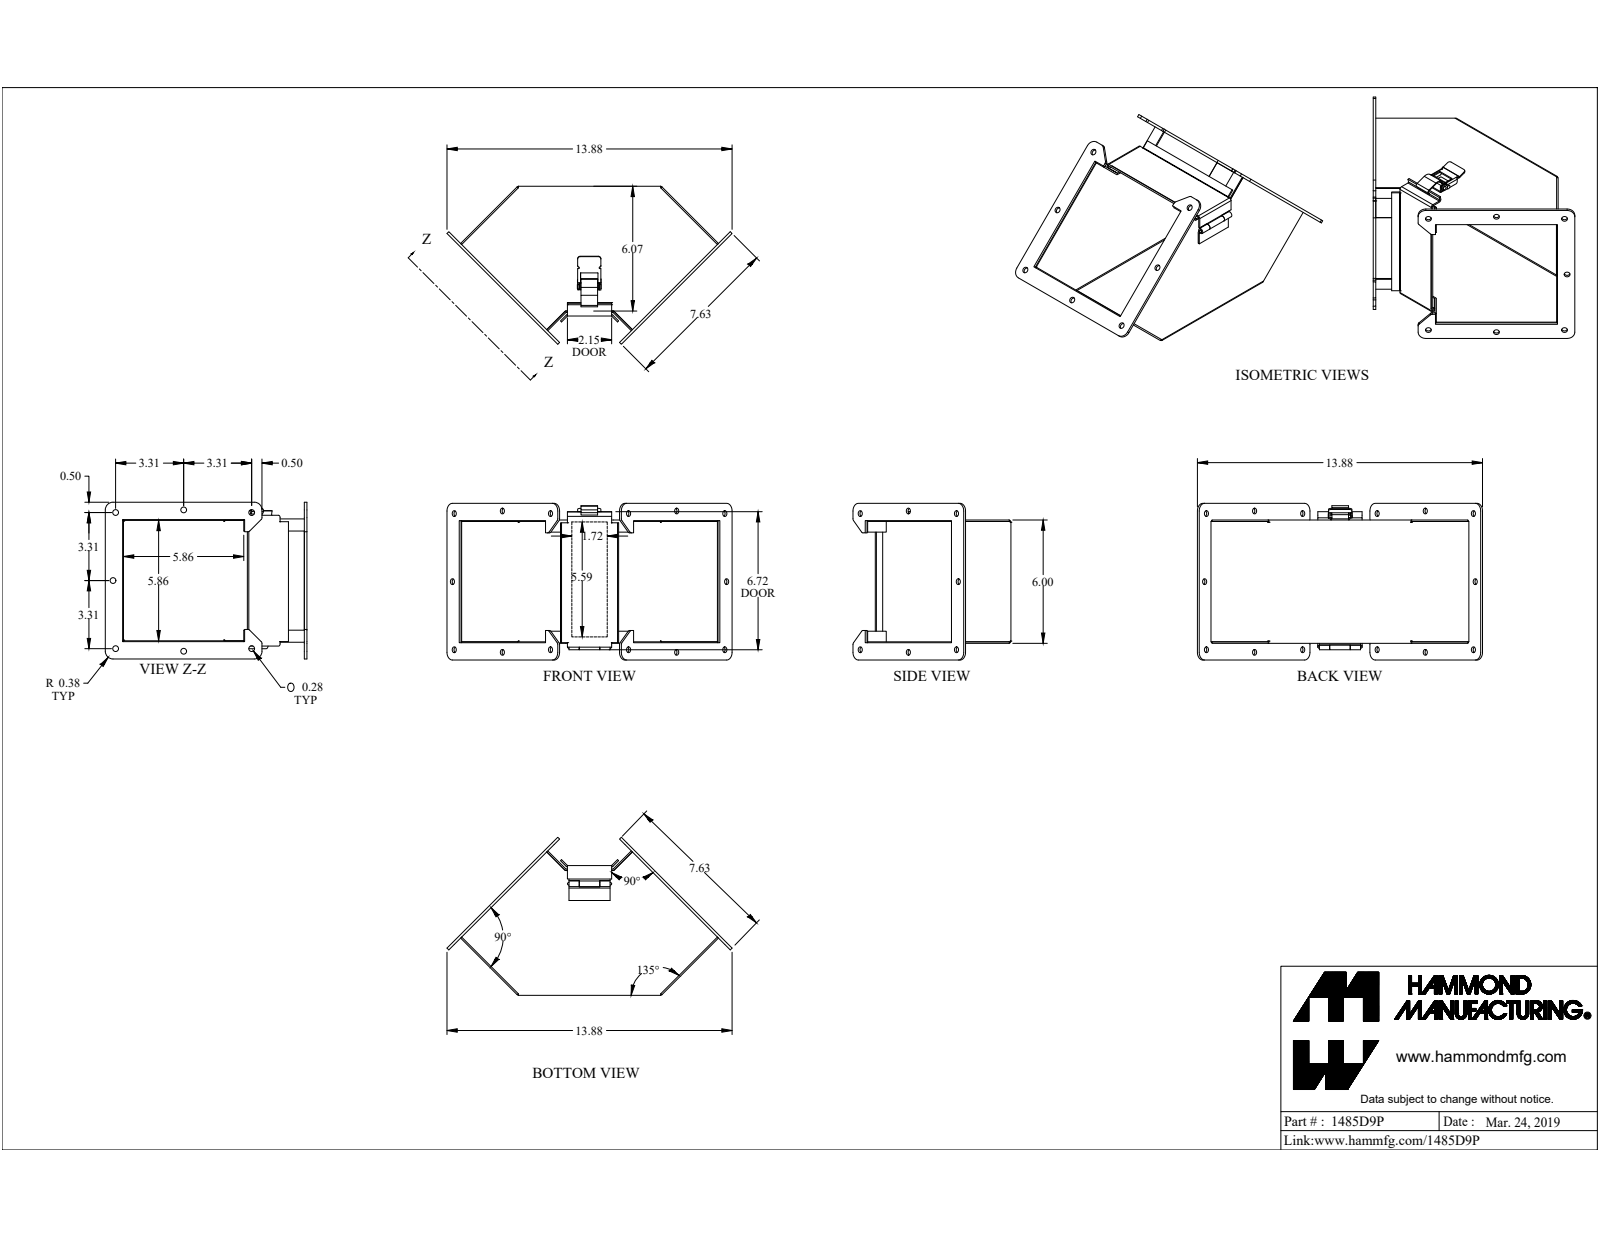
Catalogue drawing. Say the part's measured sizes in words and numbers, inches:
The part is named "1485D9P". Its 3-D file was written by "SolidWorks 2019 (CONFIG_CONTROL_DESIGN)". It is 12 solids with 339 faces: 222 planar, 115 cylindrical and 2 other. Overall it measures 13.878 by 7.688 by 7.625 inches. Its volume is 21.66 cubic inches and its surface area 574.9 square inches. Round holes: 14 of diameter 0.281, 1 of diameter 0.125, 1 of diameter 0.13, 1 of diameter 0.164. Round bosses or shafts: 2 of diameter 0.187, 1 of diameter 0.275, 1 of diameter 0.156, 1 of diameter 0.125, 1 of diameter 0.125. Partial cylindrical surfaces (rounded edges, fillets, slot ends): 11 of radius 0.036, 11 of radius 0.108, 11 of radius 0.125, 8 of radius 0.375, 7 of radius 0.016, 3 of radius 0.035, 3 of radius 0.039, 3 of radius 0.076. The main face-to-face distances are 0.072, 5.928, 6, 5.856, 8.802, 8.874, 0.125, 8.927, 8.999, 6.241. The hole center spacings are 3.315, 7.519, 4.861, 6.625, 6.625, 9.369, 3.315, 6.875.
